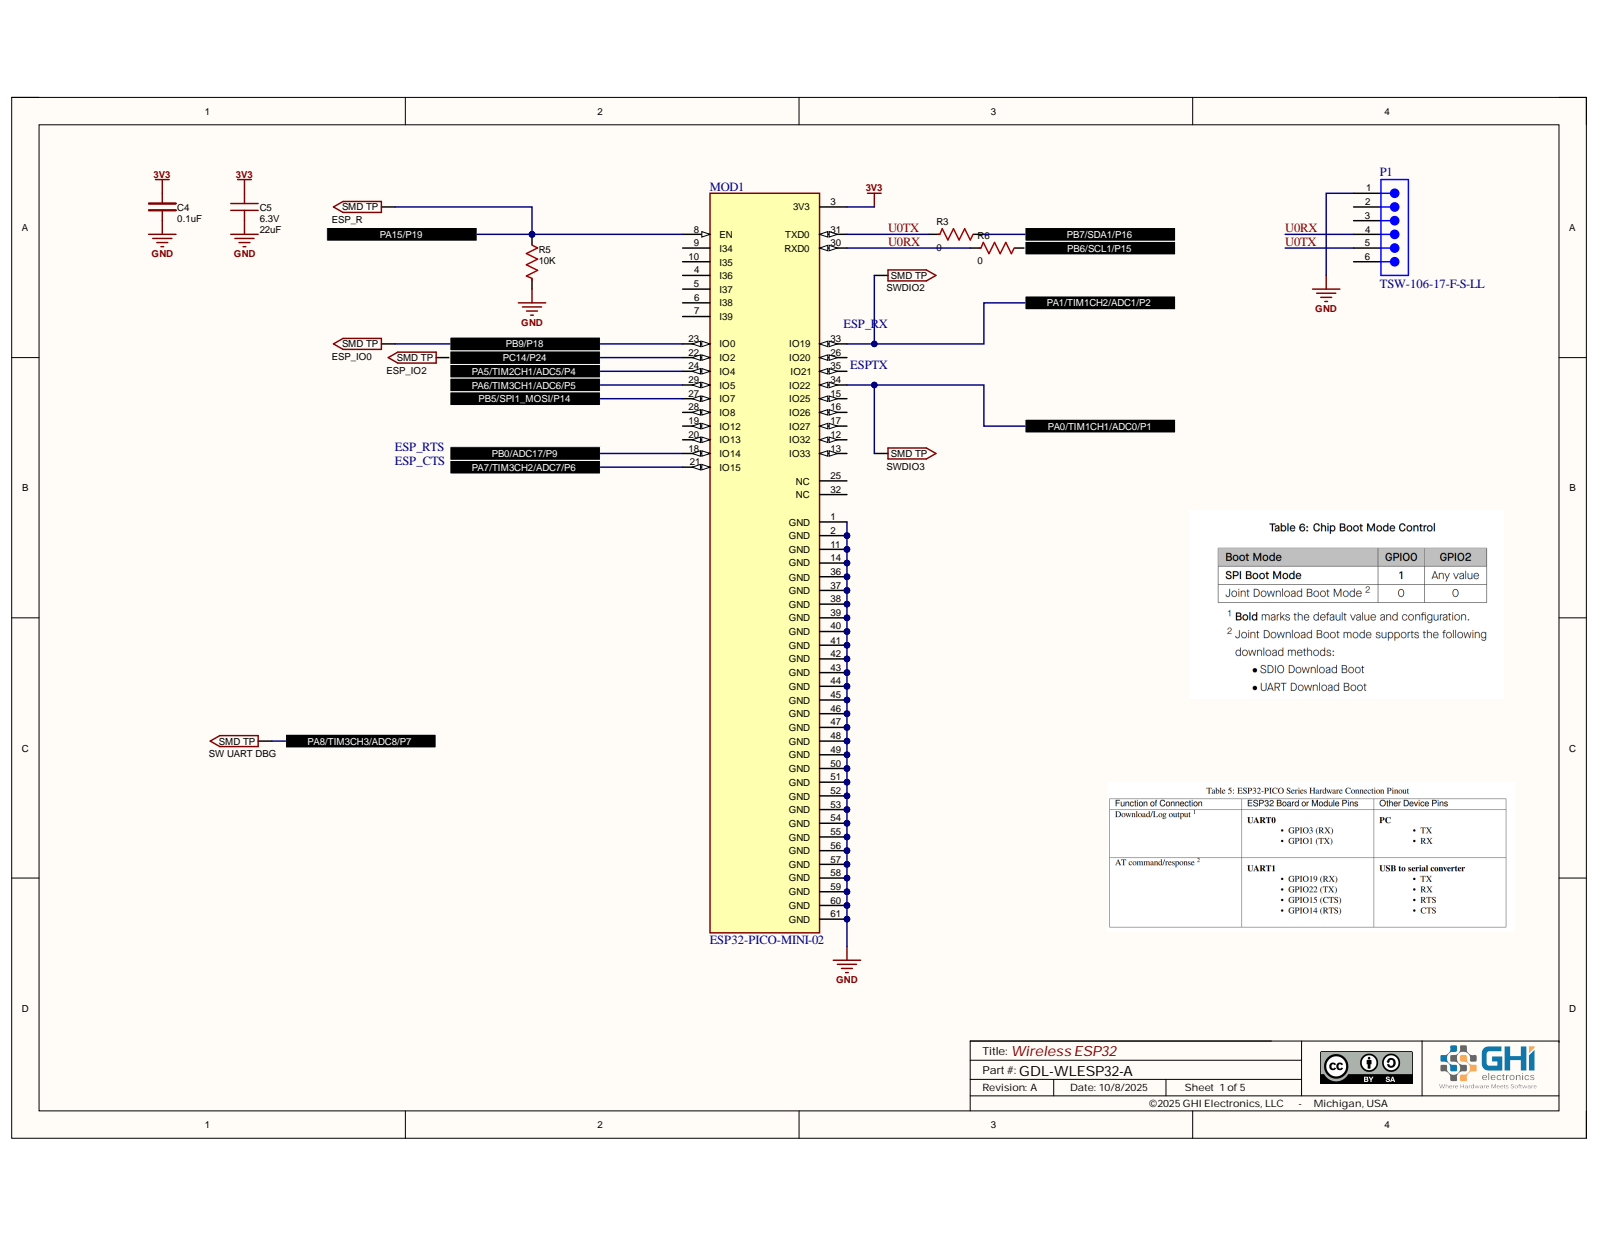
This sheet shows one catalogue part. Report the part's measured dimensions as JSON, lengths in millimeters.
{"part_name": "PCB; Board; U; DUELink-U-Connector-BM04B-SRSS-TB (+7 more)", "step_written_by": "Open CASCADE 7.5 (AUTOMOTIVE_DESIGN)", "units": "millimeters", "bodies": {"solids": 162, "faces": 2874, "planar": 2332, "cylindrical": 284, "other": 258}, "overall_size": [37, 27, 21.08], "volume_mm3": 603, "surface_area_mm2": 4235, "round_holes": [[1.02, 6], [3, 4], [1.02, 2], [0.5, 1]], "partial_cylinders_radius": [[0.12, 35], [0.15, 26], [0.1, 4], [0.25, 4], [3.5, 4], [0.17, 2], [0.18, 2], [0.18, 2]], "face_to_face_distances": [0.75, 1, 0.8, 0.95, 0.7, 2.54, 0.64, 2.4, 2.35, 2.6], "hole_center_spacings": [2.54, 5.08, 7.62, 10.16, 20, 21.81, 21.91, 22.01]}
